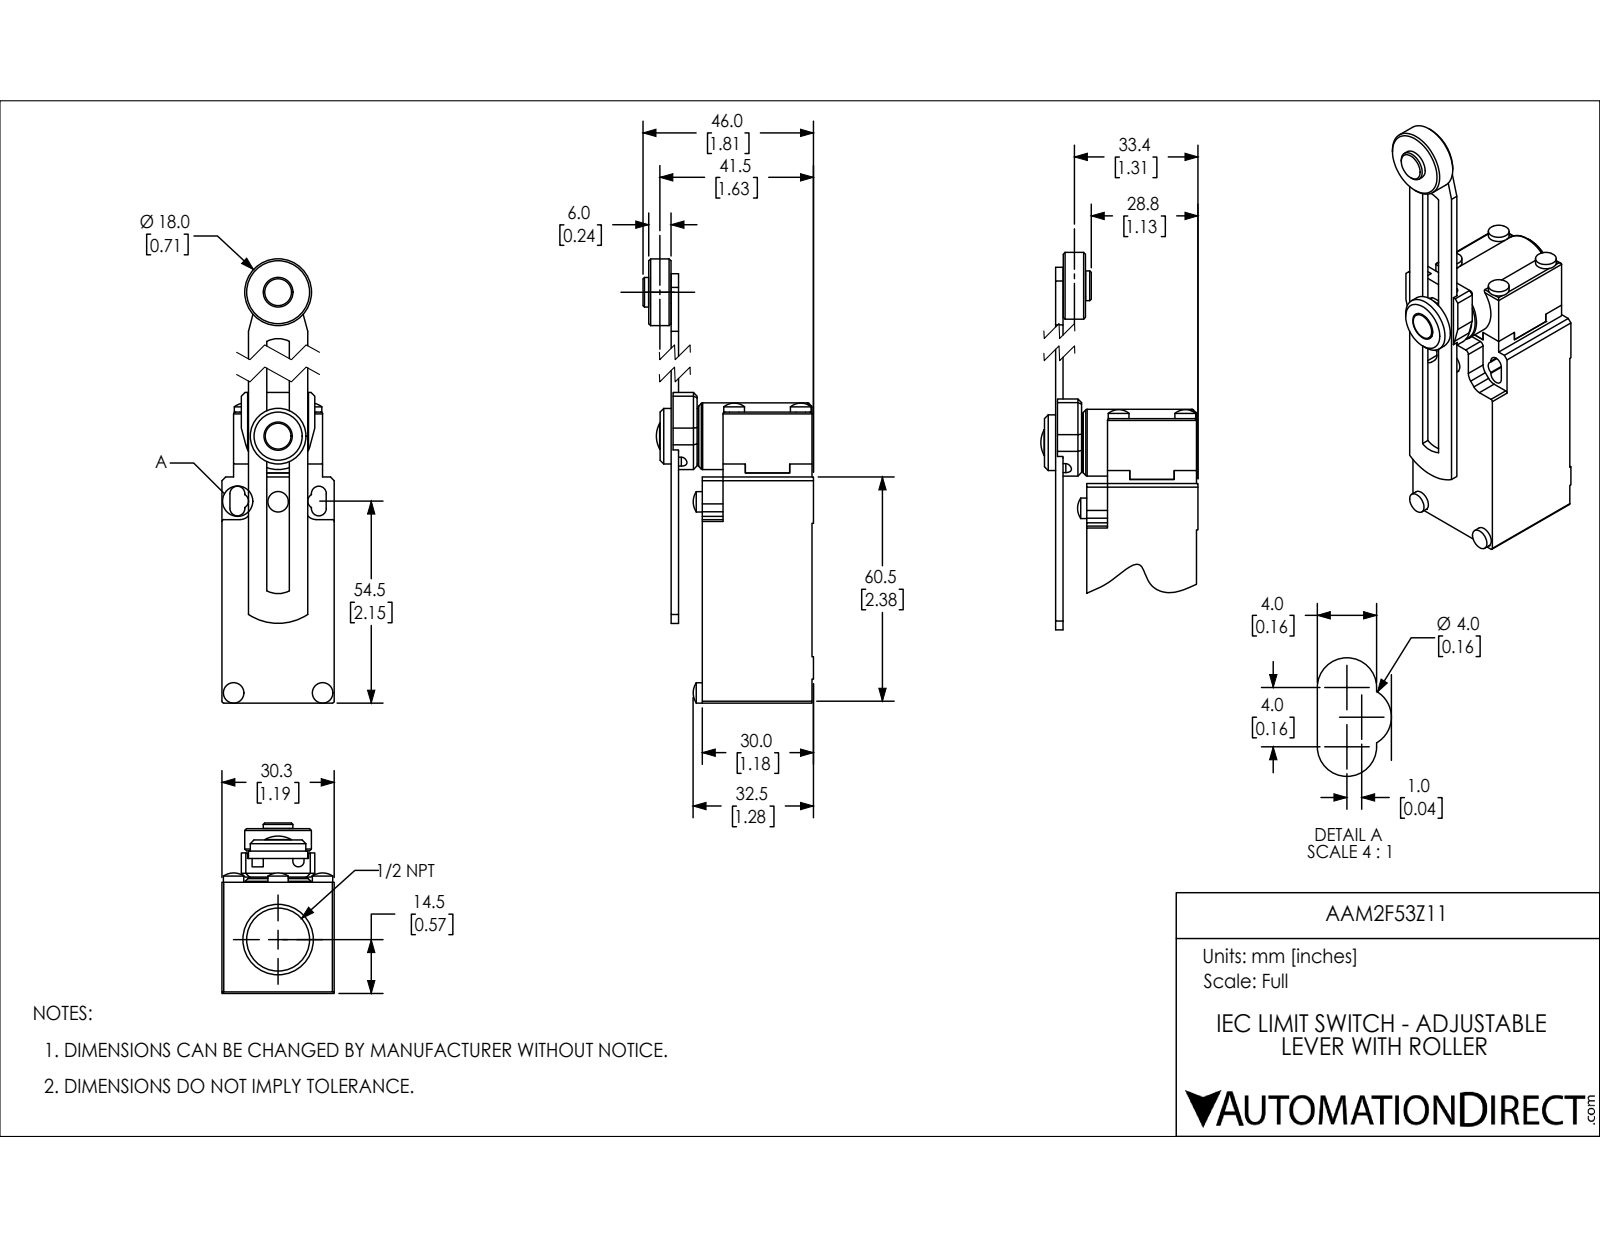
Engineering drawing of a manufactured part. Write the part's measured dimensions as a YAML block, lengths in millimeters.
part_name: "AAM2F53Z11"
step_written_by: "SolidWorks 2018 (AUTOMOTIVE_DESIGN)"
units: millimeters
bodies: {solids: 5, faces: 279, planar: 140, cylindrical: 105, other: 34}
overall_size: [136, 46, 30.3]
volume: 69510
surface_area: 19920
round_holes:
  - {diameter: 7.6, count: 1}
  - {diameter: 11, count: 1}
  - {diameter: 17, count: 1}
  - {diameter: 19, count: 1}
round_bosses_or_shafts:
  - {diameter: 5.6, count: 4}
  - {diameter: 5.5, count: 3}
  - {diameter: 18, count: 2}
  - {diameter: 15, count: 1}
  - {diameter: 8, count: 1}
  - {diameter: 7, count: 1}
  - {diameter: 6, count: 1}
partial_cylinders:
  - {radius: 0.5, count: 8}
  - {radius: 2, count: 6}
  - {radius: 3, count: 4}
  - {radius: 1, count: 2}
  - {radius: 6.5, count: 2}
  - {radius: 1.5, count: 1}
  - {radius: 4.6, count: 1}
  - {radius: 5, count: 1}
face_to_face_distances: [30.3, 29.6, 2, 6.4, 36, 38, 8.4, 3.1, 27.2, 6]
